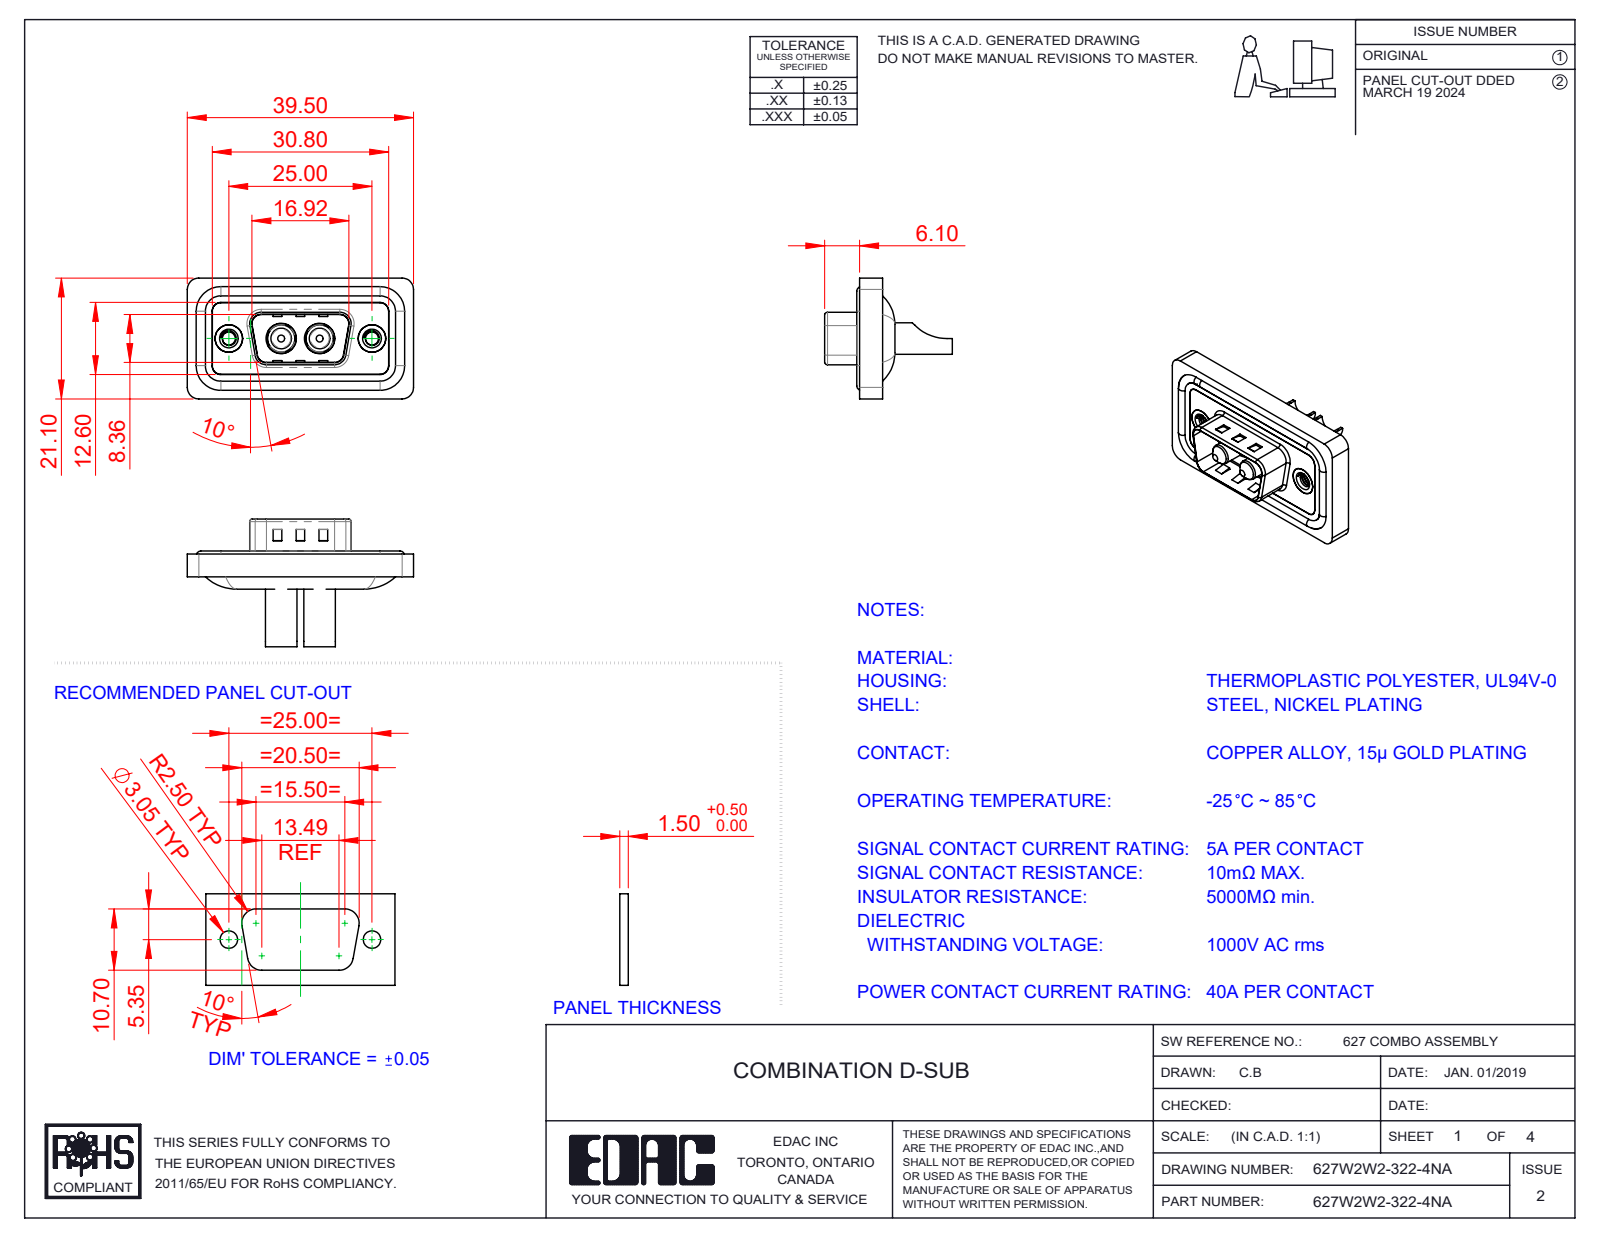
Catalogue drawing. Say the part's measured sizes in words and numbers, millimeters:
The part is named "627Combo Housing_2W2; 627W2W2-322-4NA; 627Combo Threaded Rivet_A; 627Combo Shell Rear_09 Contacts (+3 more)". Its 3-D file was written by "SolidWorks 2023 (CONFIG_CONTROL_DESIGN)". It is 11 solids with 495 faces: 169 planar, 222 cylindrical and 104 other. Overall it measures 39.5 by 22.3 by 21.1 millimeters. Its volume is 4 542 cubic millimeters and its surface area 7 261 square millimeters. Round holes: 2 of diameter 2.26, 2 of diameter 4, 2 of diameter 4.6, 2 of diameter 4.8, 2 of diameter 4.85, 2 of diameter 5, 2 of diameter 5.3. Round bosses or shafts: 4 of diameter 1.6, 2 of diameter 5.5, 2 of diameter 5.2, 2 of diameter 4.9, 2 of diameter 4.75, 2 of diameter 3.75, 2 of diameter 3.6. Partial cylindrical surfaces (rounded edges, fillets, slot ends): 22 of radius 1.5, 18 of radius 2, 8 of radius 0.5, 8 of radius 1.6, 4 of radius 0.25, 4 of radius 0.6, 4 of radius 0.65, 4 of radius 0.9. The main face-to-face distances are 0.4, 1.1, 2.9, 3.1, 0.5, 1.6, 1.5, 2.5, 0.7, 4. The hole center spacings are 9.14, 15.86, 6.72, 25.
